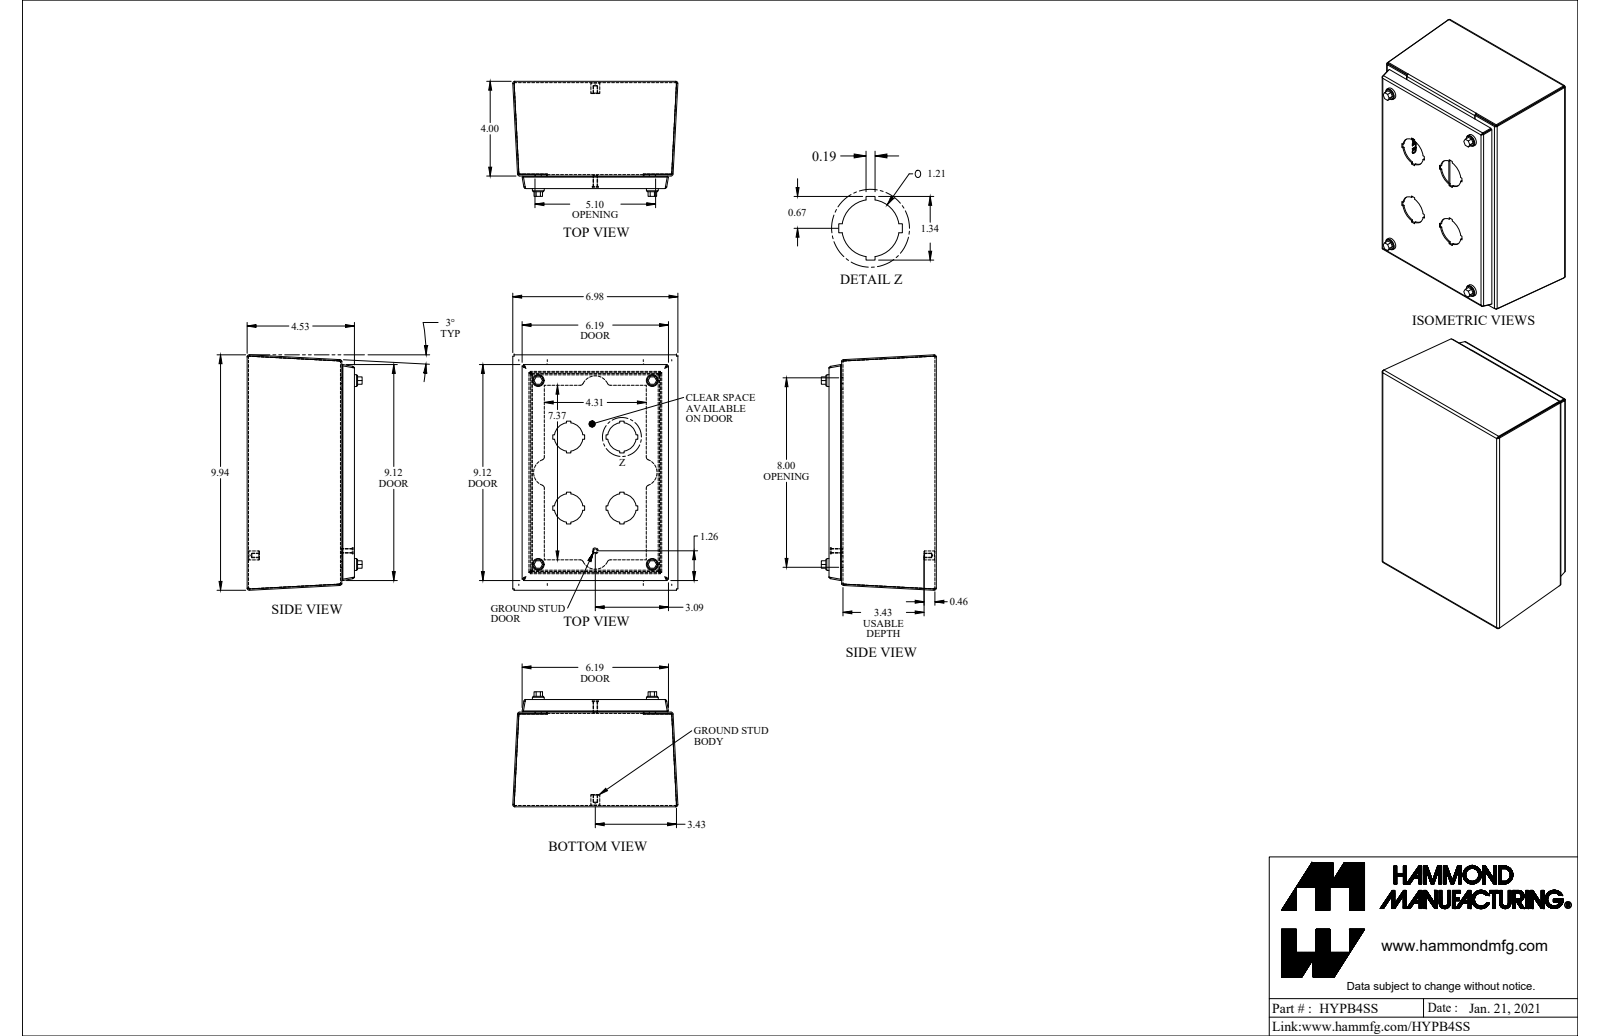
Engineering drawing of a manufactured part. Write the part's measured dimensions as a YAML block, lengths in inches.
part_name: "HYPB4SS"
step_written_by: "SolidWorks 2021 (AUTOMOTIVE_DESIGN)"
units: inches
bodies: {solids: 22, faces: 515, planar: 344, cylindrical: 148, other: 23}
overall_size: [9.942, 6.976, 4.859]
volume: 21.45
surface_area: 691
round_holes:
  - {diameter: 0.065, count: 4}
  - {diameter: 0.239, count: 4}
  - {diameter: 0.24, count: 4}
  - {diameter: 0.25, count: 4}
  - {diameter: 0.253, count: 4}
  - {diameter: 0.4, count: 4}
  - {diameter: 1.21, count: 4}
  - {diameter: 0.235, count: 2}
  - {diameter: 0.235, count: 2}
  - {diameter: 0.156, count: 1}
round_bosses_or_shafts:
  - {diameter: 0.375, count: 5}
  - {diameter: 0.19, count: 5}
  - {diameter: 0.5, count: 4}
  - {diameter: 0.45, count: 4}
  - {diameter: 0.406, count: 4}
  - {diameter: 0.315, count: 4}
  - {diameter: 0.25, count: 1}
partial_cylinders:
  - {radius: 0.029, count: 16}
  - {radius: 0.086, count: 16}
  - {radius: 0.125, count: 12}
  - {radius: 0.055, count: 4}
  - {radius: 0.076, count: 4}
  - {radius: 0.5, count: 4}
  - {radius: 0.575, count: 4}
face_to_face_distances: [0.057, 4.418, 4.475, 0.057, 4.532, 4.475, 3.943, 0.475, 4, 0.532]
hole_center_spacings: [9.139, 7.766, 7.766, 2.707, 4.819, 4.263, 4.819, 5.534]
